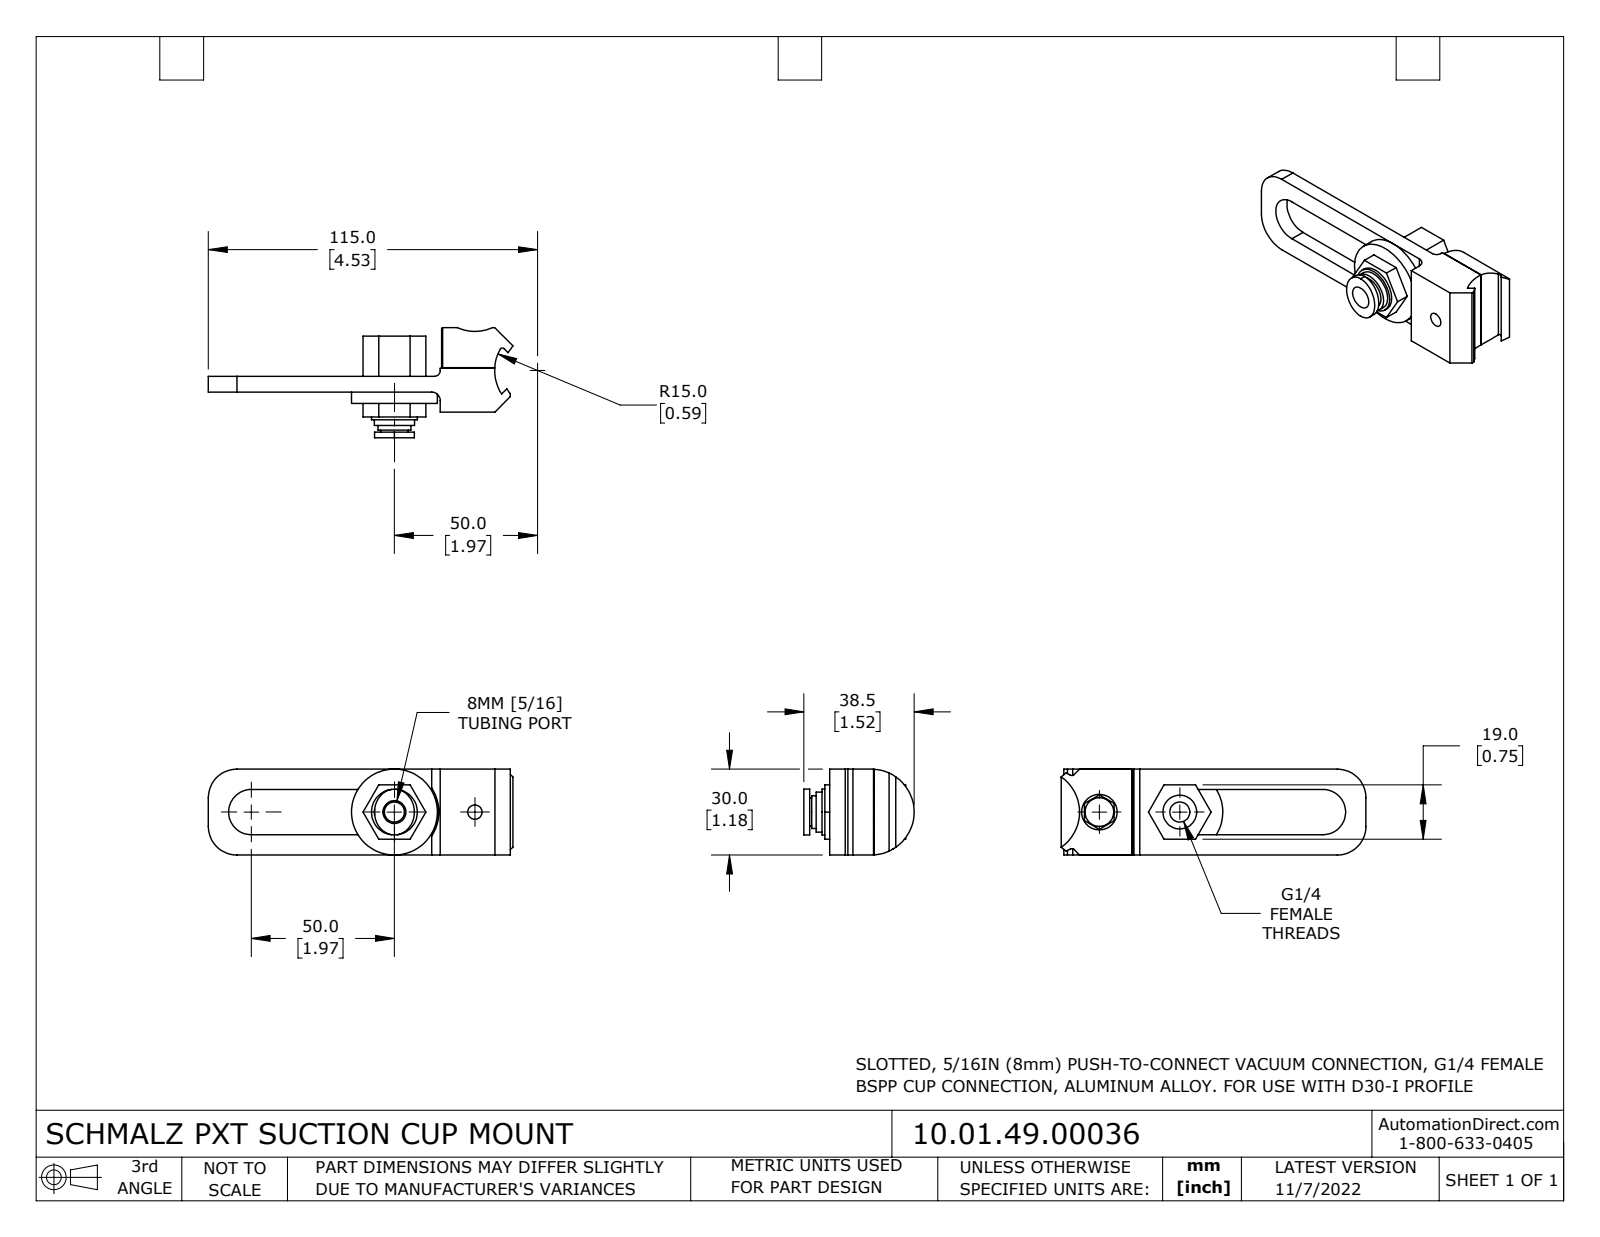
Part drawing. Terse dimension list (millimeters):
name: 10.01.49.00036
written by: SolidWorks 2021 (CONFIG_CONTROL_DESIGN)
unit: mm
bodies: 5 solids, 111 faces (58 planar, 49 cylindrical, 4 other)
size: 106.4 × 38.5 × 30
volume: 31 409 mm³; area: 16 634 mm²
holes: 1× ⌀5, 1× ⌀6.6, 1× ⌀7, 1× ⌀8, 1× ⌀10, 1× ⌀11.8, 1× ⌀12.4, 1× ⌀16.5
bosses: 1× ⌀30, 1× ⌀16, 1× ⌀14, 1× ⌀13.84, 1× ⌀11.45, 1× ⌀9.7, 1× ⌀6
rounds: 2× R7.9, 2× R10, 2× R15, 1× R0.8, 1× R2, 1× R3, 1× R9.25, 1× R11
face distances: 5.5, 3, 12.5, 4, 9.5, 19, 30, 7, 2.8, 12.3
hole spacings: 28.1
